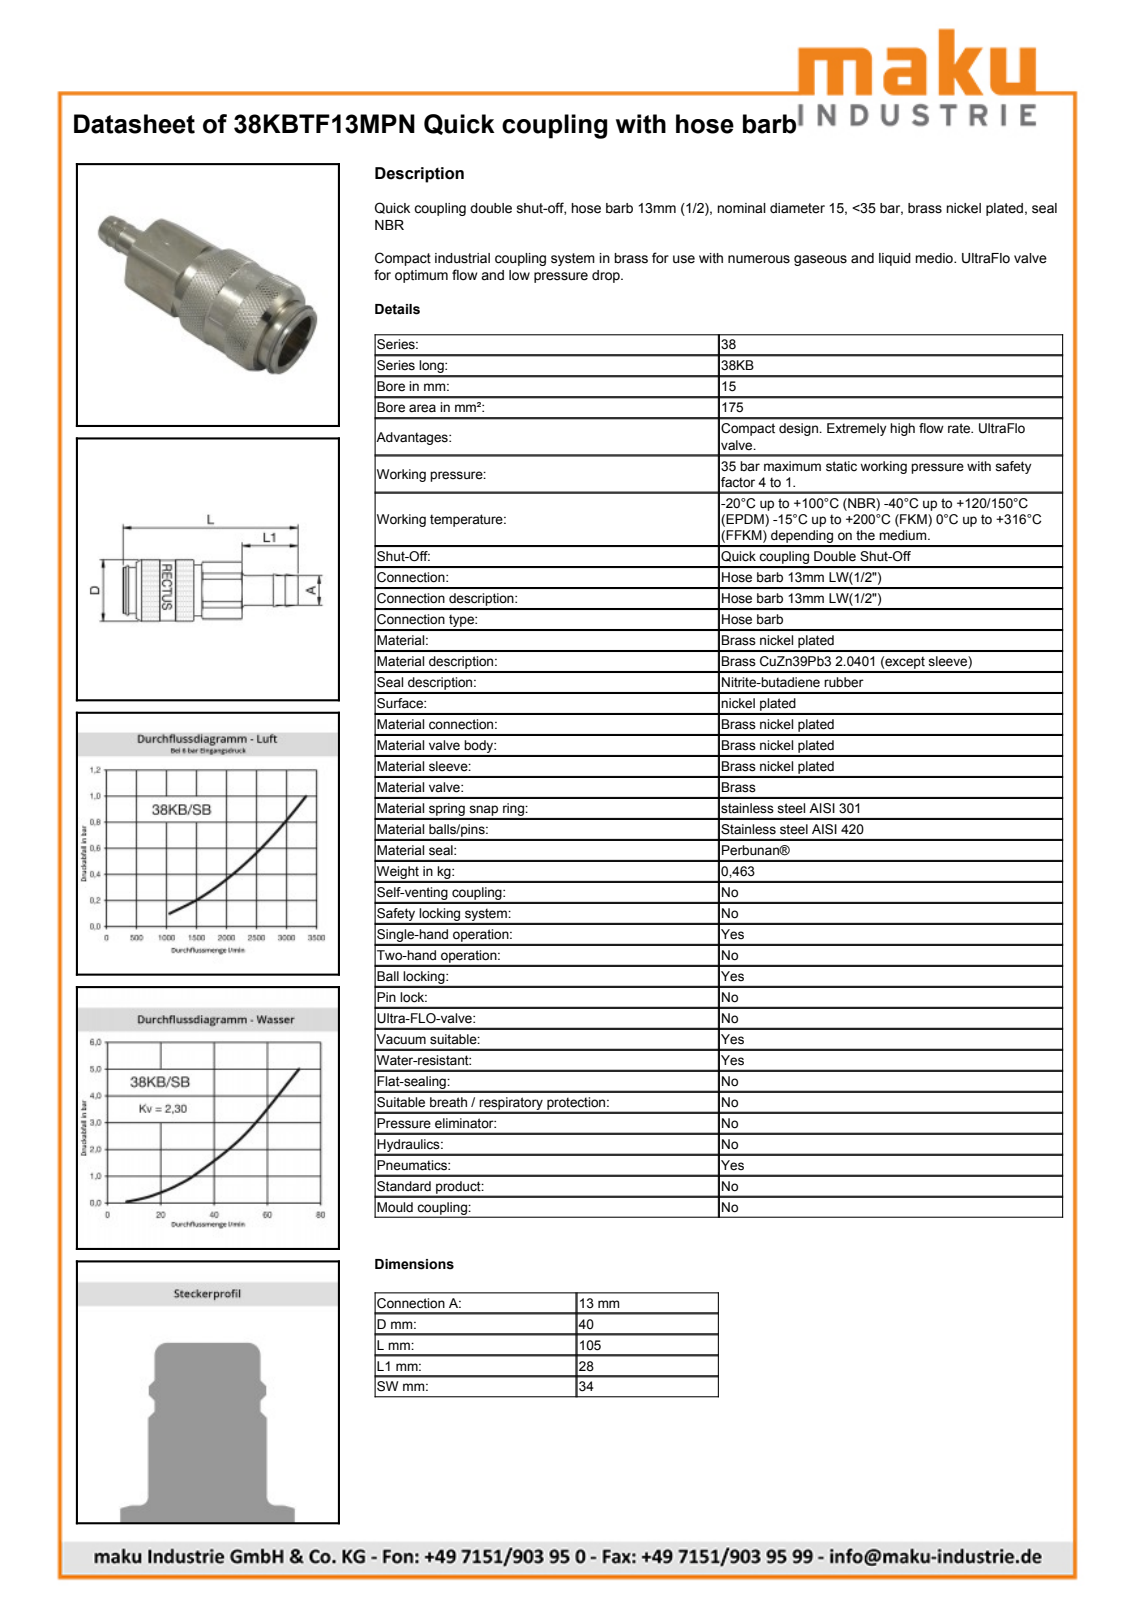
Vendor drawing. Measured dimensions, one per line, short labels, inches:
name: D110623
written by: Autodesk Inventor 2013 (AUTOMOTIVE_DESIGN)
unit: in
bodies: 2 solids, 526 faces (187 planar, 75 cylindrical, 264 other)
size: 4.215 × 1.575 × 1.575
volume: 5.108 in³; area: 33.49 in²
holes: 1× ⌀1.181, 1× ⌀1.211, 1× ⌀1.356, 1× ⌀1.362
bosses: 1× ⌀1.575, 1× ⌀1.535, 1× ⌀1.339, 1× ⌀1.122, 1× ⌀1.102, 1× ⌀0.514
rounds: 1× R0.526, 1× R0.728, 1× R0.764
face distances: 1.339, 3.112, 0.321, 2.791, 1.945, 1.167, 0.846, 1.577, 1.256, 0.409
